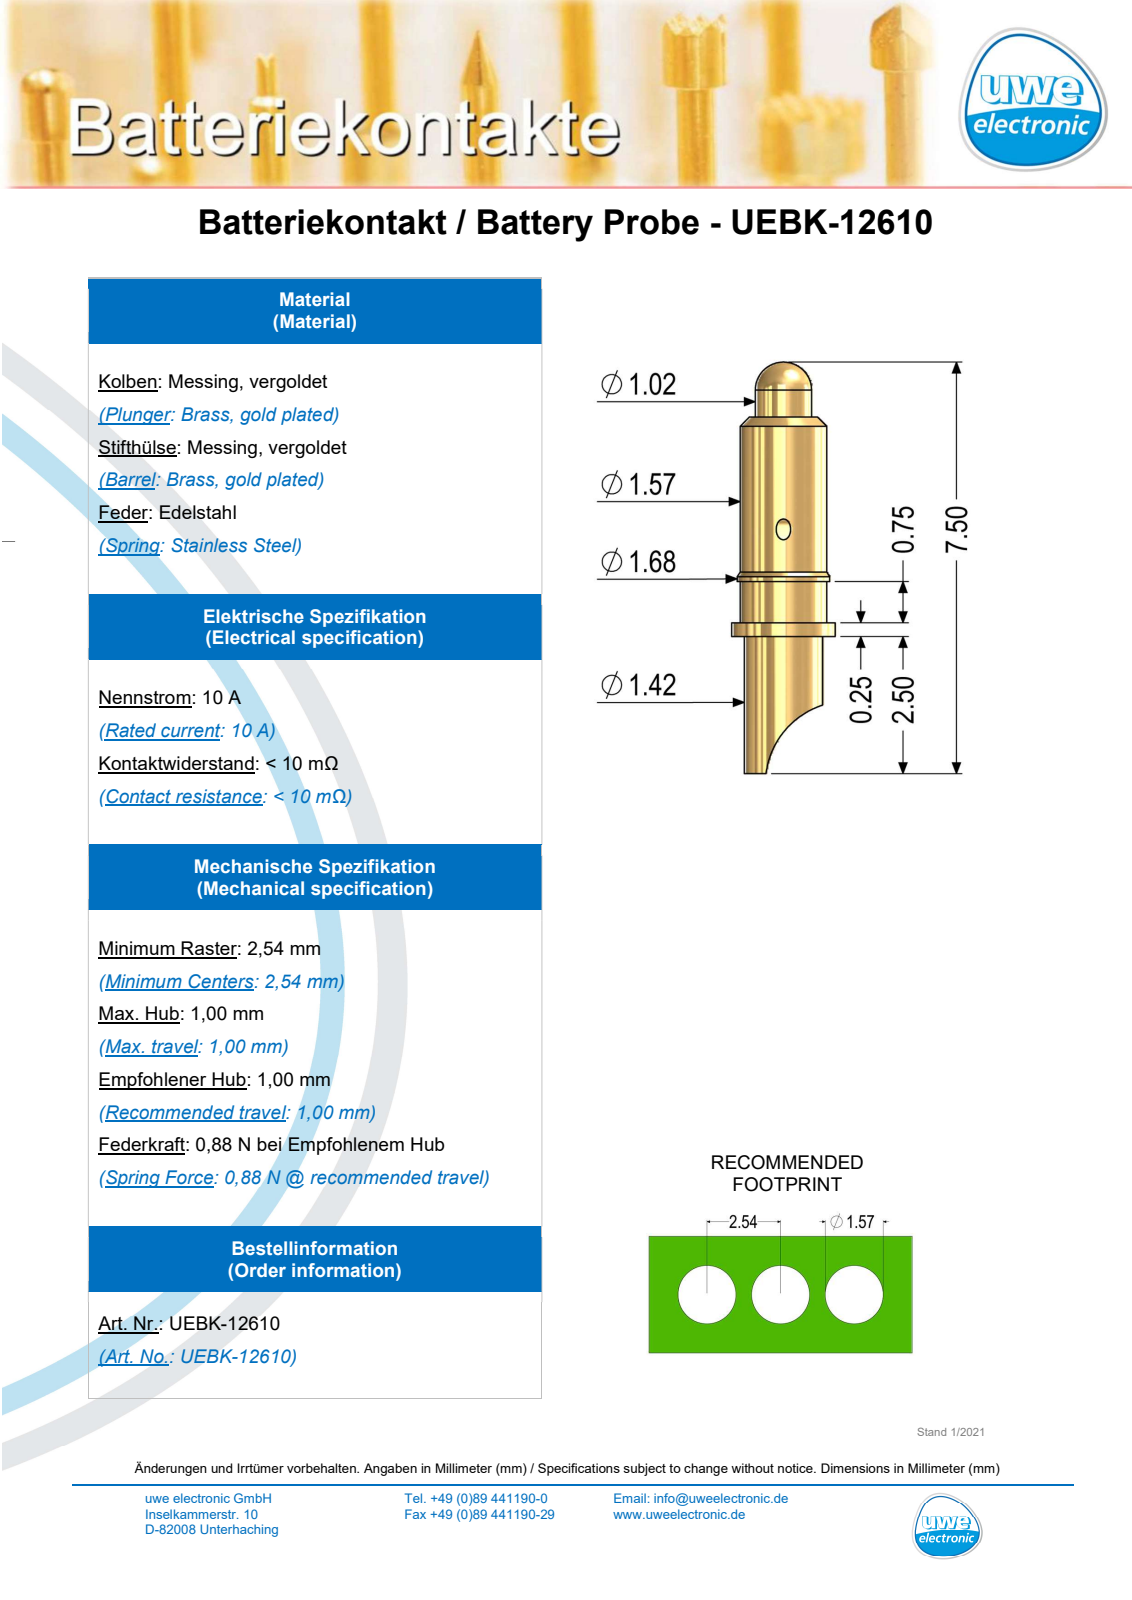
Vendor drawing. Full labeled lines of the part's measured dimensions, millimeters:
Part name (STEP PRODUCT): UEBK-12610_2017_09_12
STEP written by: SolidWorks 2017 (AUTOMOTIVE_DESIGN)
Units: millimetres
Bodies: 1 solid, 33 faces (6 planar, 16 cylindrical, 11 other)
Overall size (bounding box): 7.5 × 1.88 × 1.88
Volume: 10 mm³ · Surface area: 42 mm²
Round holes (diameter × count): ⌀1.2 ×1
Round bosses / shafts (diameter × count): ⌀1.88 ×1, ⌀1.68 ×1, ⌀1.57 ×1, ⌀1.42 ×1, ⌀1.02 ×1
Partial cylindrical surfaces — rounded edges, fillets, slot ends (radius × count): R0.15 ×1, R1.51 ×1
Main face-to-face distances: 4, 3.75, 1, 0.75, 3, 2.5, 2.75, 3.5, 6.5
